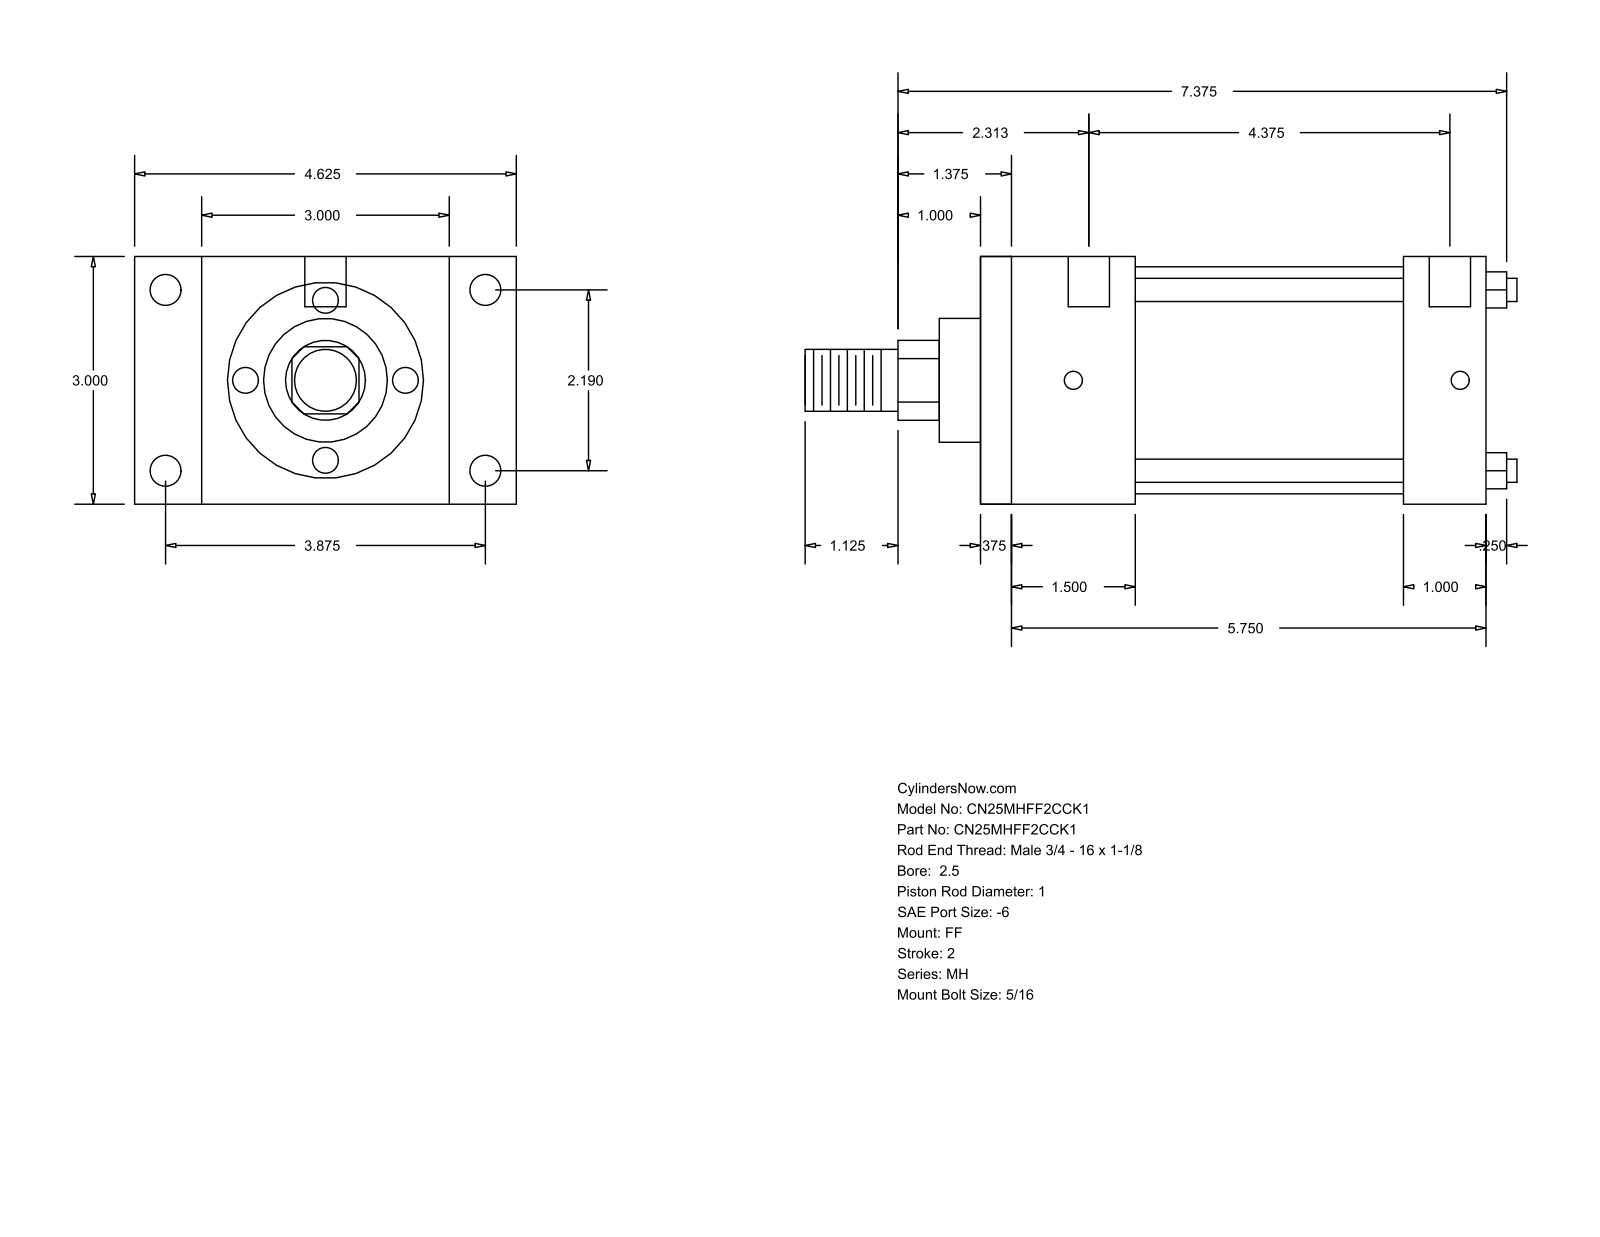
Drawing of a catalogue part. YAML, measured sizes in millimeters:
part_name: "MH_FF__0250_1"
step_written_by: "GSSL Pune (CONFIG_CONTROL_DESIGN)"
units: millimeters
bodies: {solids: 0, faces: 92, planar: 64, cylindrical: 28, other: 0}
overall_size: [219.07, 117.47, 76.2]
round_holes:
  - {diameter: 5.56, count: 4}
  - {diameter: 9.53, count: 4}
  - {diameter: 12.7, count: 2}
round_bosses_or_shafts:
  - {diameter: 7.14, count: 4}
  - {diameter: 69.85, count: 1}
  - {diameter: 38.1, count: 1}
  - {diameter: 25.4, count: 1}
  - {diameter: 19.05, count: 1}
partial_cylinders:
  - {radius: 12.29, count: 1}
face_to_face_distances: [76.2, 155.57, 9.52, 146.05, 25.4, 47.63, 130.17, 38.11, 120.65, 82.54]
hole_center_spacings: [55.62, 98.42, 113.05, 119.06, 3.18, 4.76, 111.12, 114.3]
